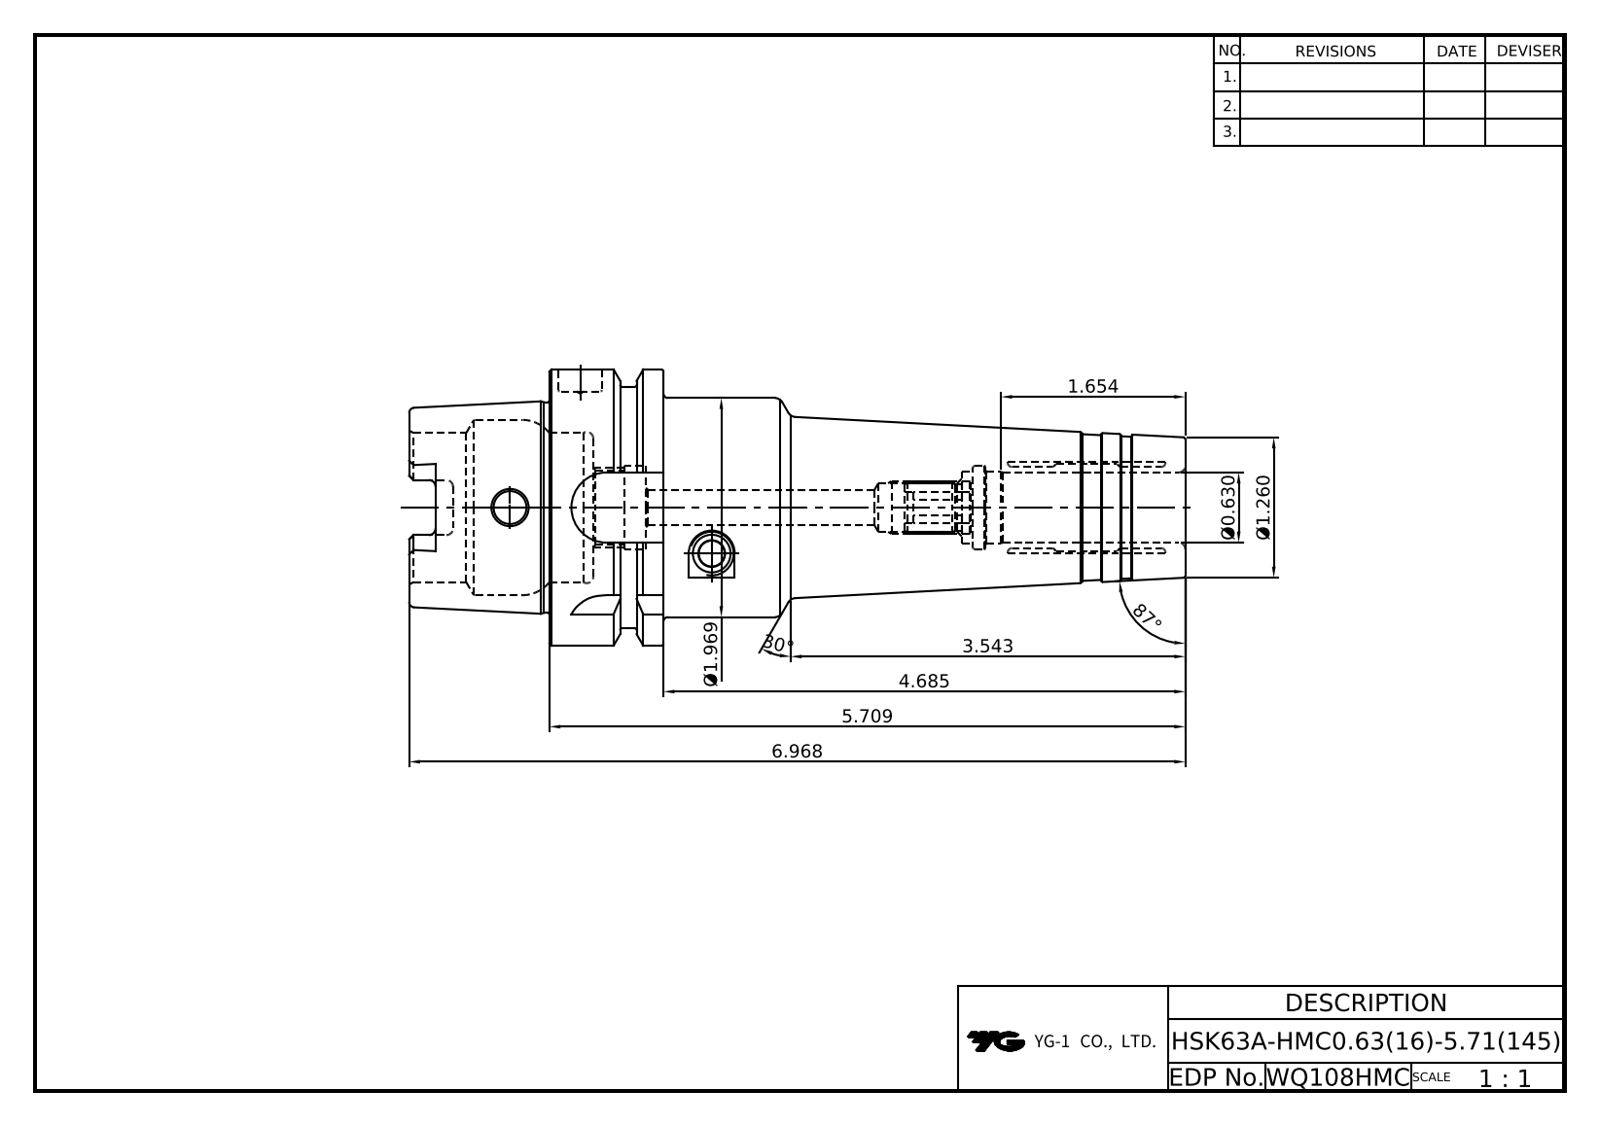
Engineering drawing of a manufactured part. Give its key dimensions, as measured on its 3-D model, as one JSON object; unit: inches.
{"part_name": "WQ108HMC-HSK63A-HMC0_63-5_71", "step_written_by": "PRO/ENGINEER BY PARAMETRIC TECHNOLOGY CORPORATION, 2012130 (CONFIG_CONTROL_DESIGN)", "units": "inches", "bodies": {"solids": 1, "faces": 217, "planar": 58, "cylindrical": 55, "other": 104}, "overall_size": [6.969, 2.48, 2.48], "volume_in3": 13.31, "surface_area_in2": 64.25, "round_holes": [[0.295, 1], [0.315, 1], [0.394, 1], [0.437, 1], [0.63, 1], [0.646, 1], [0.669, 1], [0.709, 1], [0.748, 1], [1.339, 1], [1.575, 1]], "round_bosses_or_shafts": [[2.48, 1], [2.165, 1], [1.969, 1], [1.891, 1]], "partial_cylinders_radius": [[0.059, 6], [0.113, 4], [0.315, 4]], "face_to_face_distances": [1.024, 0.394, 0.63, 5.709, 5.315, 4.685, 1.26, 1.654, 2.283, 6.969]}
